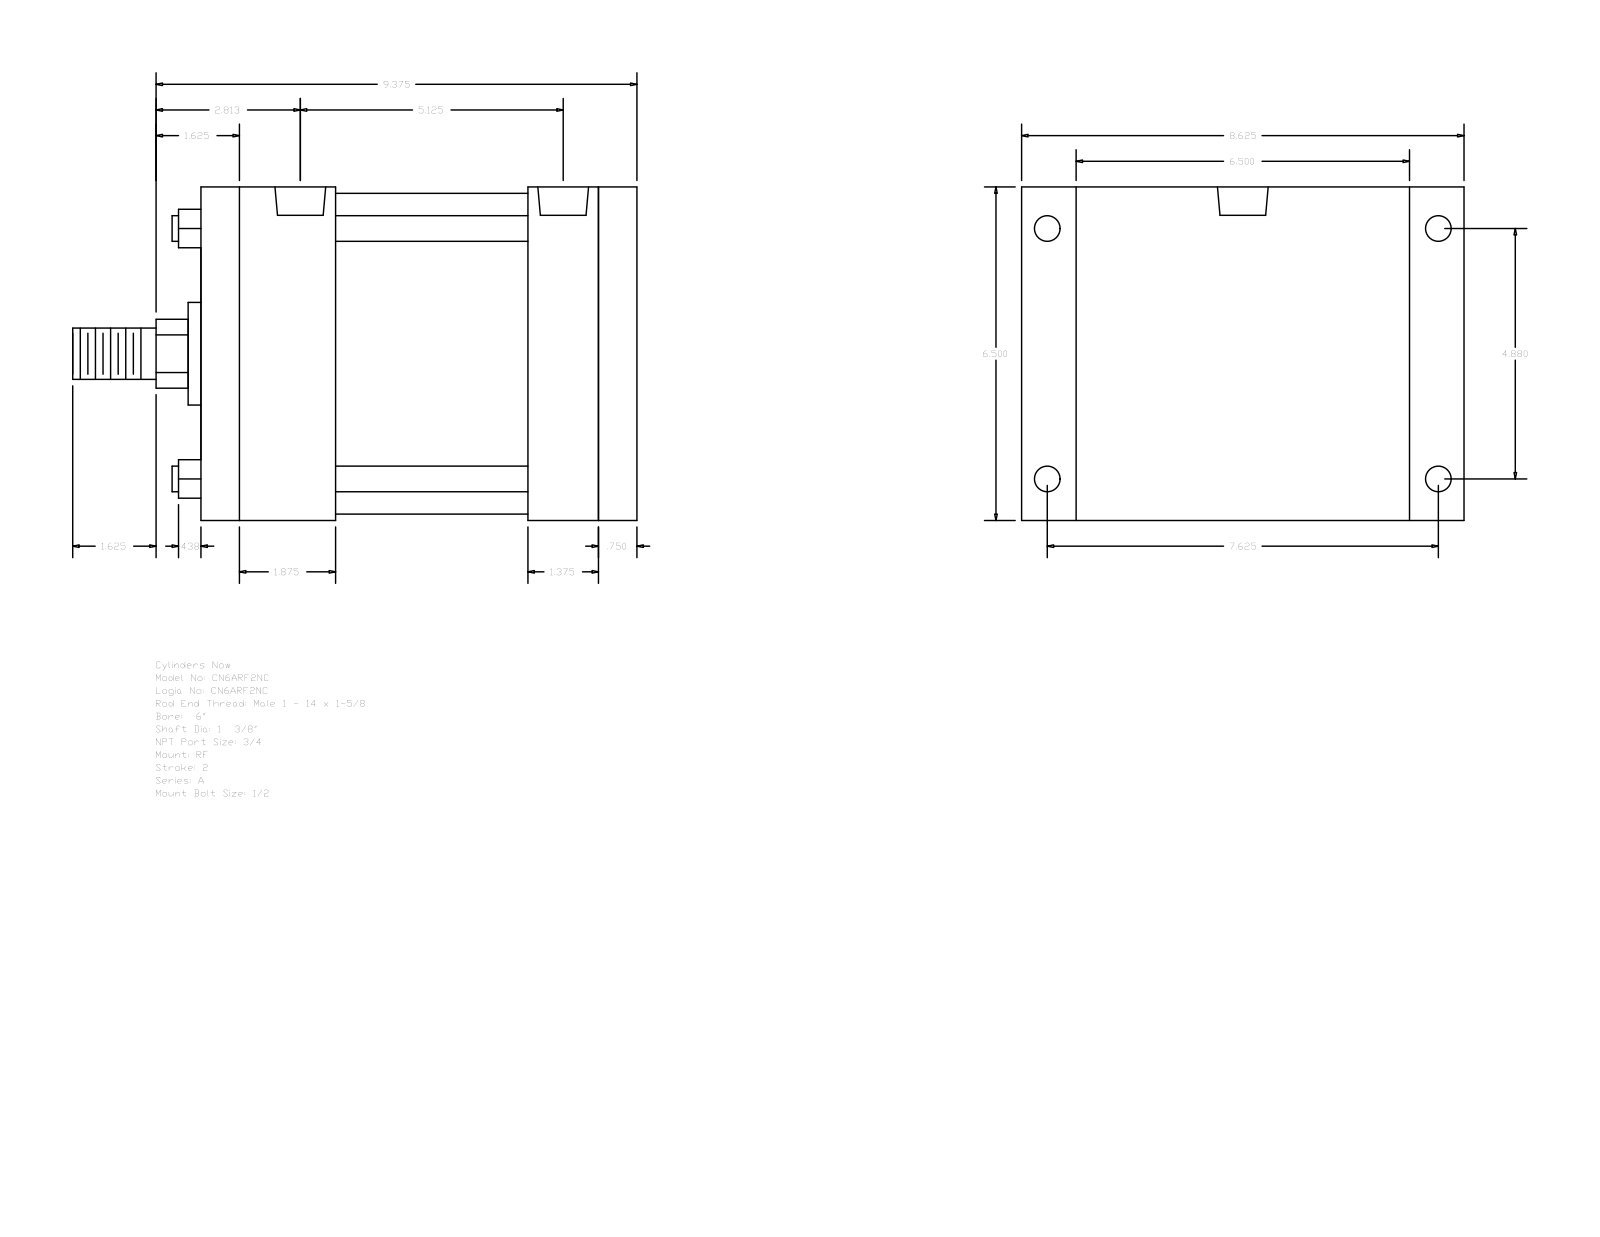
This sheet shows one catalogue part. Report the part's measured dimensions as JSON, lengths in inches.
{"part_name": "A_RF__0600_1.375", "step_written_by": "GSSL Pune (CONFIG_CONTROL_DESIGN)", "units": "inches", "bodies": {"solids": 0, "faces": 92, "planar": 64, "cylindrical": 28, "other": 0}, "overall_size": [11, 8.625, 6.5], "round_holes": [[0.5, 4], [0.594, 4], [0.989, 2]], "round_bosses_or_shafts": [[0.5, 4], [6.25, 1], [2, 1], [1.375, 1], [1, 1]], "partial_cylinders_radius": [[0.672, 1]], "face_to_face_distances": [6.5, 8.5, 0.75, 7.75, 5.125, 3.75, 2.125, 2.625, 5.875, 6.375], "hole_center_spacings": [0.219, 4.687, 4.88, 4.906, 7.625, 9.053, 5.125]}
